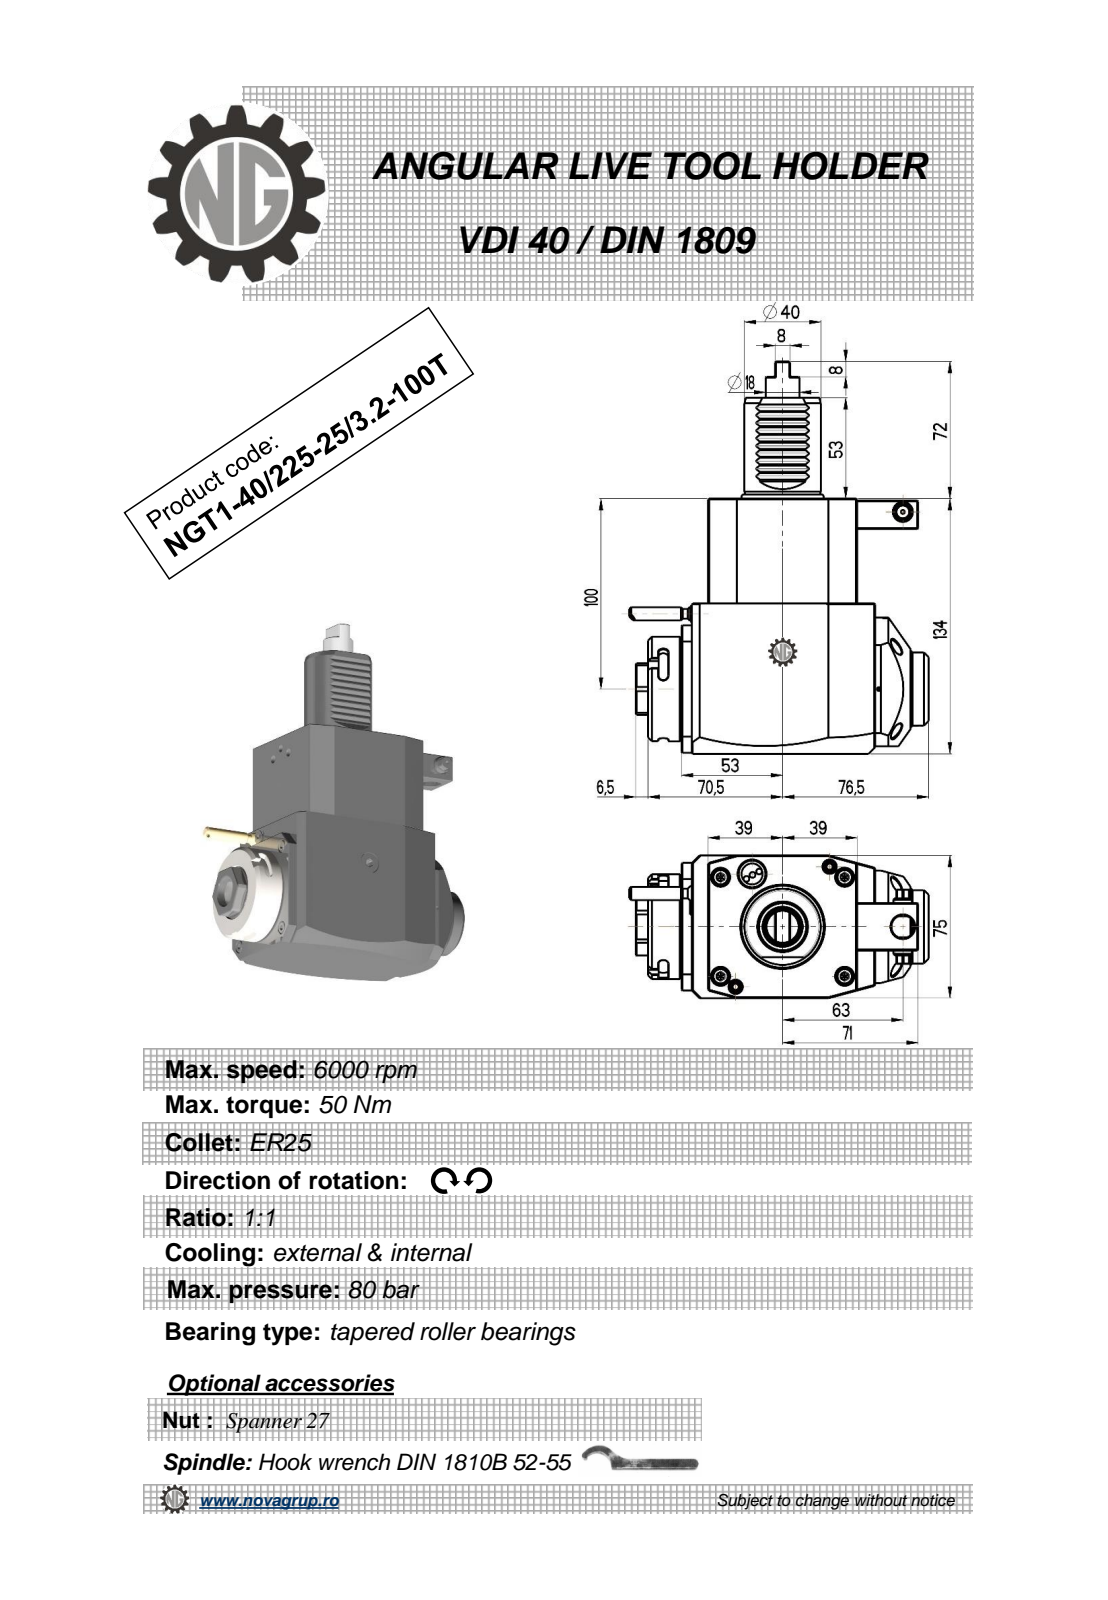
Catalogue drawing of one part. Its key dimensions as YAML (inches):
part_name: "NGT1_40_225_25_3_2_100T"
step_written_by: "PRO/ENGINEER BY PARAMETRIC TECHNOLOGY CORPORATION, 2010280 (CONFIG_CONTROL_DESIGN)"
units: inches
bodies: {solids: 1, faces: 351, planar: 183, cylindrical: 92, other: 76}
overall_size: [8.11, 6.174, 2.953]
volume: 65.6
surface_area: 119.8
round_holes:
  - {diameter: 0.079, count: 1}
  - {diameter: 0.098, count: 1}
  - {diameter: 0.118, count: 1}
  - {diameter: 0.177, count: 1}
  - {diameter: 0.374, count: 1}
  - {diameter: 0.472, count: 1}
  - {diameter: 0.709, count: 1}
round_bosses_or_shafts:
  - {diameter: 0.315, count: 2}
  - {diameter: 2.165, count: 1}
  - {diameter: 1.89, count: 1}
  - {diameter: 1.575, count: 1}
  - {diameter: 1.516, count: 1}
  - {diameter: 0.701, count: 1}
  - {diameter: 0.394, count: 1}
  - {diameter: 0.276, count: 1}
partial_cylinders:
  - {radius: 0.012, count: 10}
  - {radius: 0.098, count: 6}
  - {radius: 0.031, count: 2}
  - {radius: 7.087, count: 2}
  - {radius: 0.02, count: 1}
  - {radius: 0.152, count: 1}
  - {radius: 0.167, count: 1}
  - {radius: 0.591, count: 1}
face_to_face_distances: [2.953, 5.276, 3.071, 0.551, 3.622, 0.689, 1.24, 3.342, 4.311, 2.126]
hole_center_spacings: [1.701, 2.197, 3.642]
